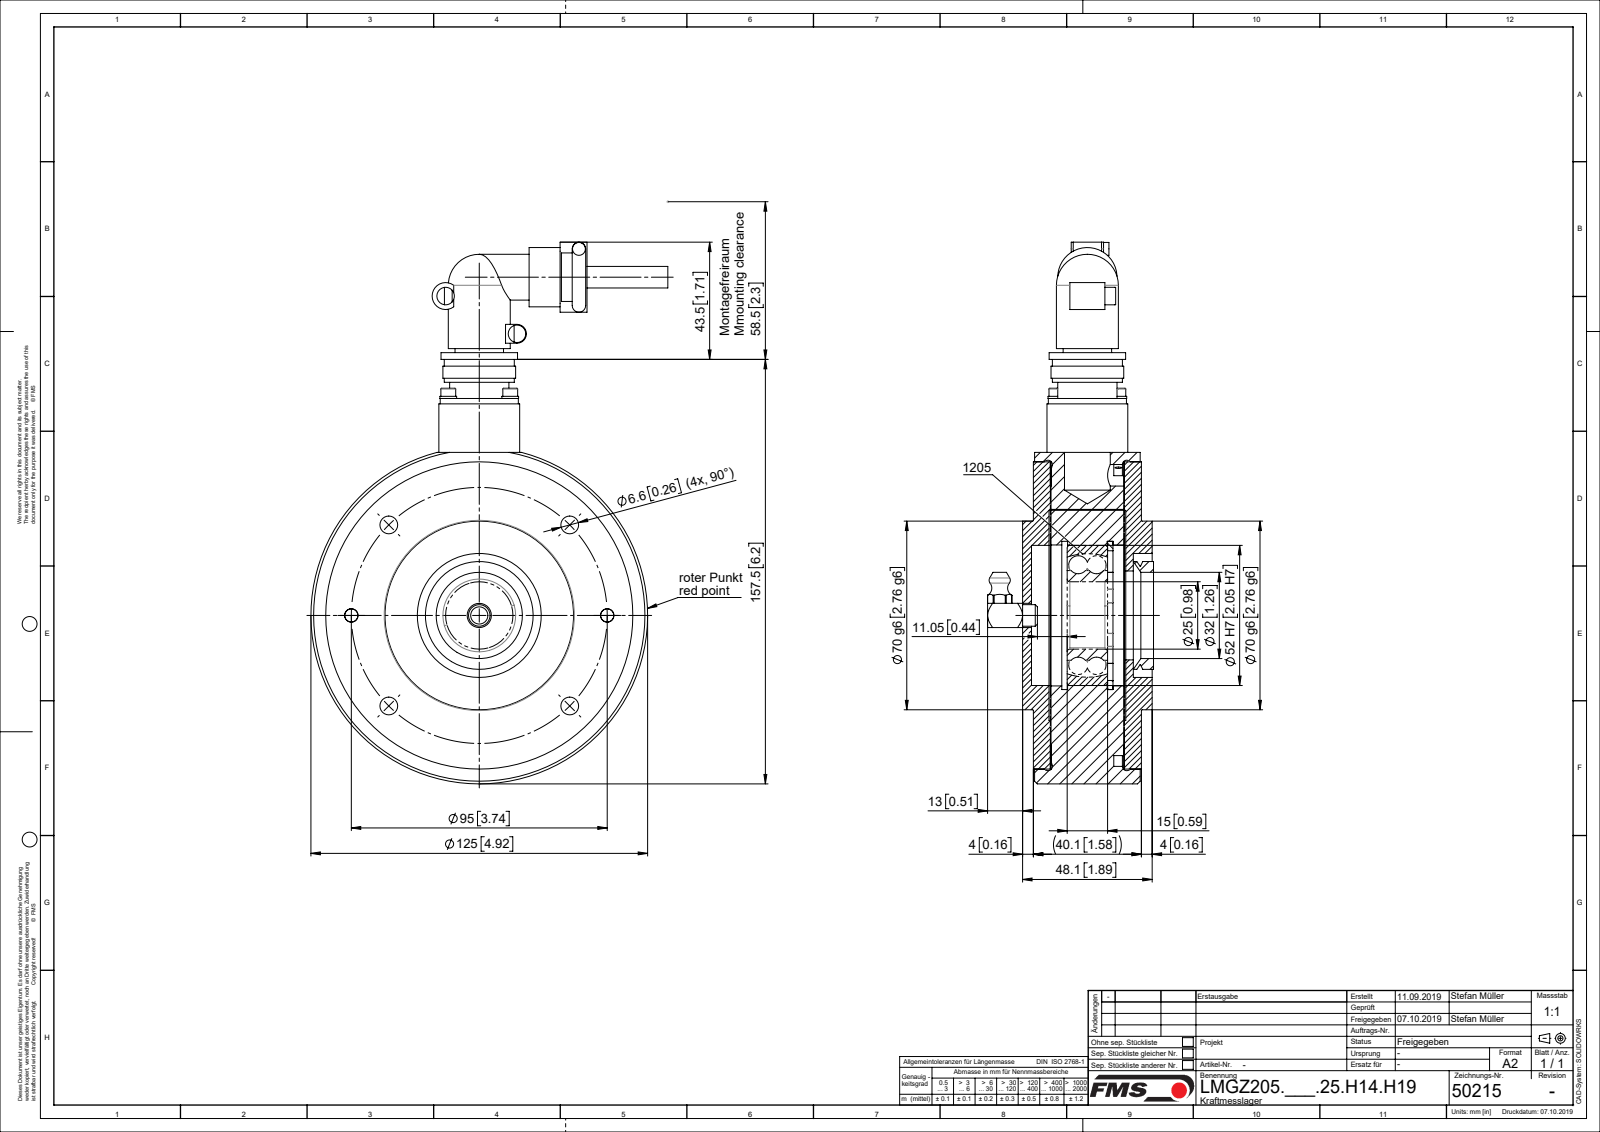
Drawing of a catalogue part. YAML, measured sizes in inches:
part_name: "ZEICHNUNG7; L50215; L4832404; L47955 (+8 more)"
step_written_by: "Mechanical Desktop 2007 (CONFIG_CONTROL_DESIGN)"
units: inches
bodies: {solids: 21, faces: 438, planar: 129, cylindrical: 248, other: 61}
overall_size: [7.913, 5.217, 2.465]
volume: 30.05
surface_area: 228.7
round_holes:
  - {diameter: 0.26, count: 6}
  - {diameter: 0.102, count: 4}
  - {diameter: 0.126, count: 4}
  - {diameter: 0.134, count: 4}
  - {diameter: 0.138, count: 4}
  - {diameter: 0.197, count: 2}
  - {diameter: 0.433, count: 2}
  - {diameter: 0.342, count: 1}
  - {diameter: 0.906, count: 1}
  - {diameter: 0.984, count: 1}
  - {diameter: 1.22, count: 1}
  - {diameter: 1.299, count: 1}
round_bosses_or_shafts:
  - {diameter: 0.244, count: 4}
  - {diameter: 0.217, count: 4}
  - {diameter: 0.118, count: 4}
  - {diameter: 0.394, count: 3}
  - {diameter: 0.866, count: 2}
  - {diameter: 0.315, count: 2}
  - {diameter: 0.256, count: 2}
  - {diameter: 0.236, count: 2}
partial_cylinders:
  - {radius: 0.197, count: 9}
  - {radius: 0.098, count: 2}
  - {radius: 0.138, count: 1}
  - {radius: 1.594, count: 1}
  - {radius: 1.85, count: 1}
face_to_face_distances: [1.073, 1.321, 0.248, 0.258, 1.331, 1.063, 1.083, 0.157, 0.415, 1.488]
hole_center_spacings: [1.87, 0.64, 0.906, 1.431, 2.645, 3.456, 1.281, 3.741]
